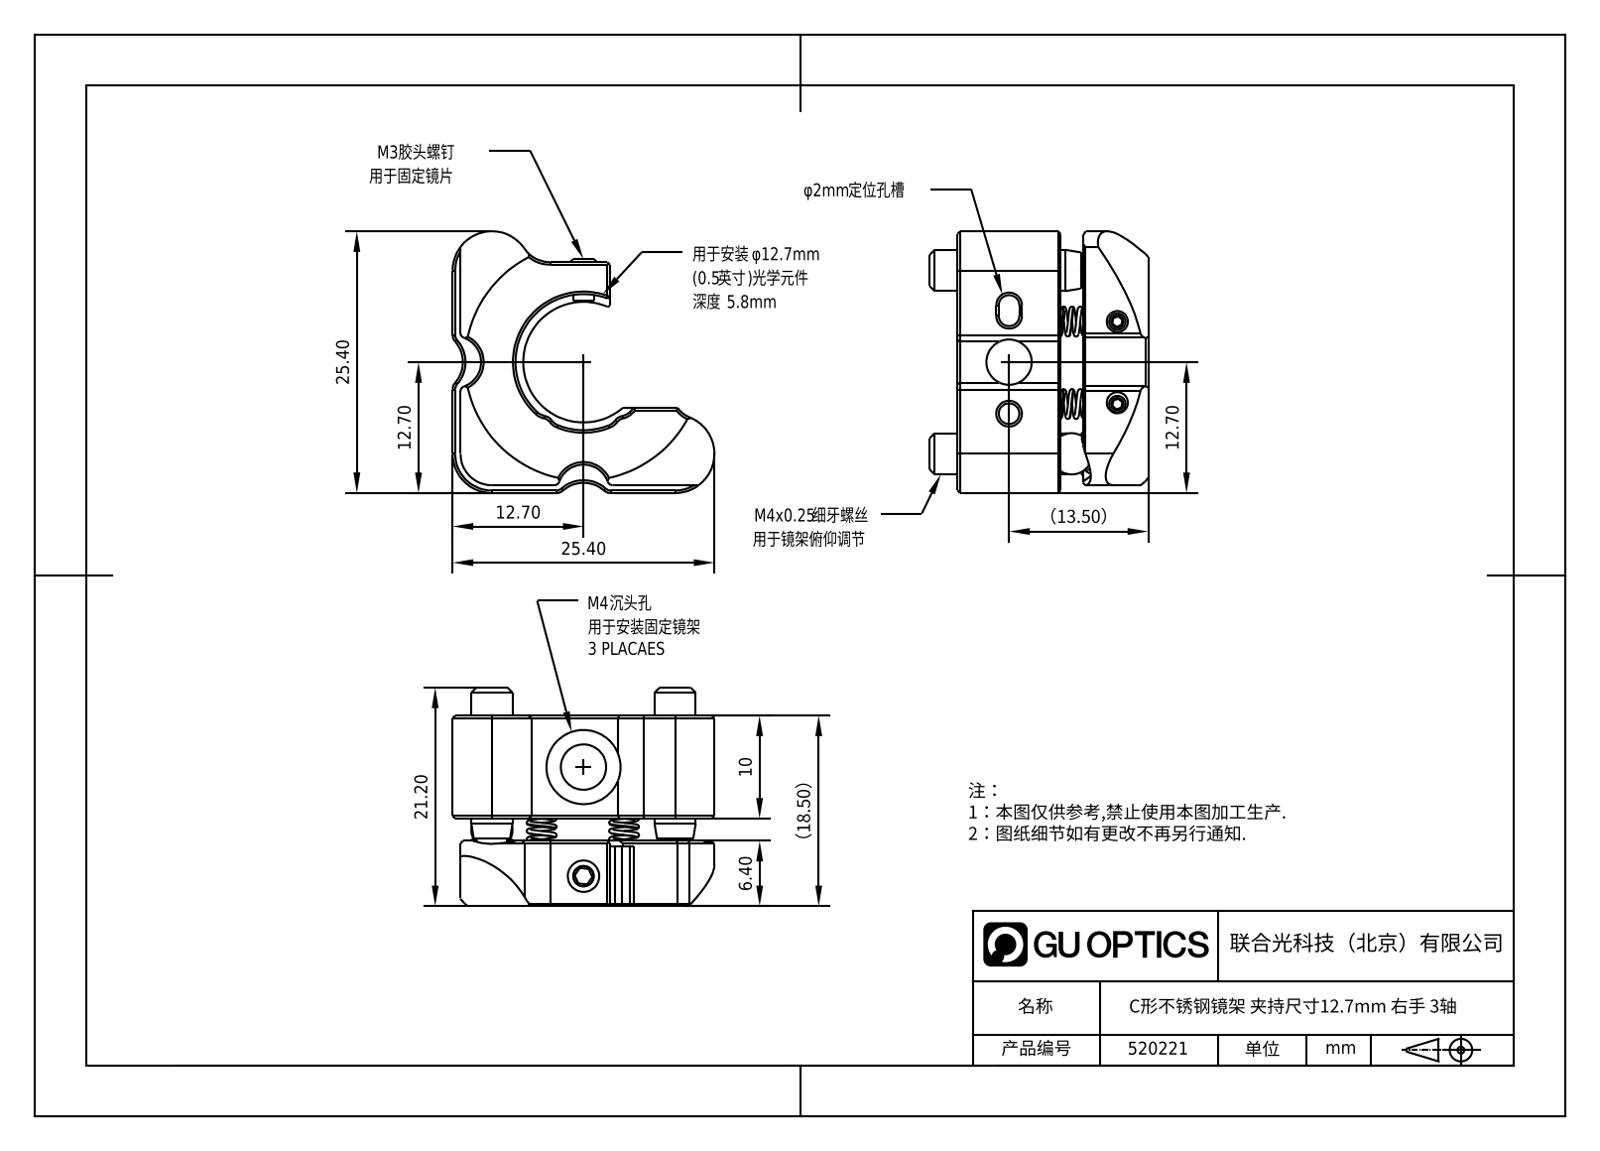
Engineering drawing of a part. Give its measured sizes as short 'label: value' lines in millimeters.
name: 520221
written by: SolidWorks 2020 (CONFIG_CONTROL_DESIGN)
unit: mm
bodies: 25 solids, 413 faces (183 planar, 91 cylindrical, 139 other)
size: 25.4 × 25.4 × 21.22
volume: 3 856 mm³; area: 5 579 mm²
holes: 4× ⌀1.6, 4× ⌀3.2, 4× ⌀3.4, 3× ⌀2.99, 3× ⌀3.75, 3× ⌀4.35, 2× ⌀2, 2× ⌀4.4, 2× ⌀7.2, 1× ⌀2.5
bosses: 6× ⌀2.6, 5× ⌀2, 3× ⌀4, 2× ⌀1.5, 1× ⌀3
rounds: 8× R1, 4× R0.5, 4× R1.5, 3× R2.5, 3× R3, 3× R3.81, 2× R1.15, 2× R5
face distances: 2, 10, 8.35, 18.35, 6.35, 12, 0.76, 5.62, 0.5, 7.62
hole spacings: 4.95, 12.83, 7.87, 7.88, 11.07, 13.76, 7.01, 13.75
